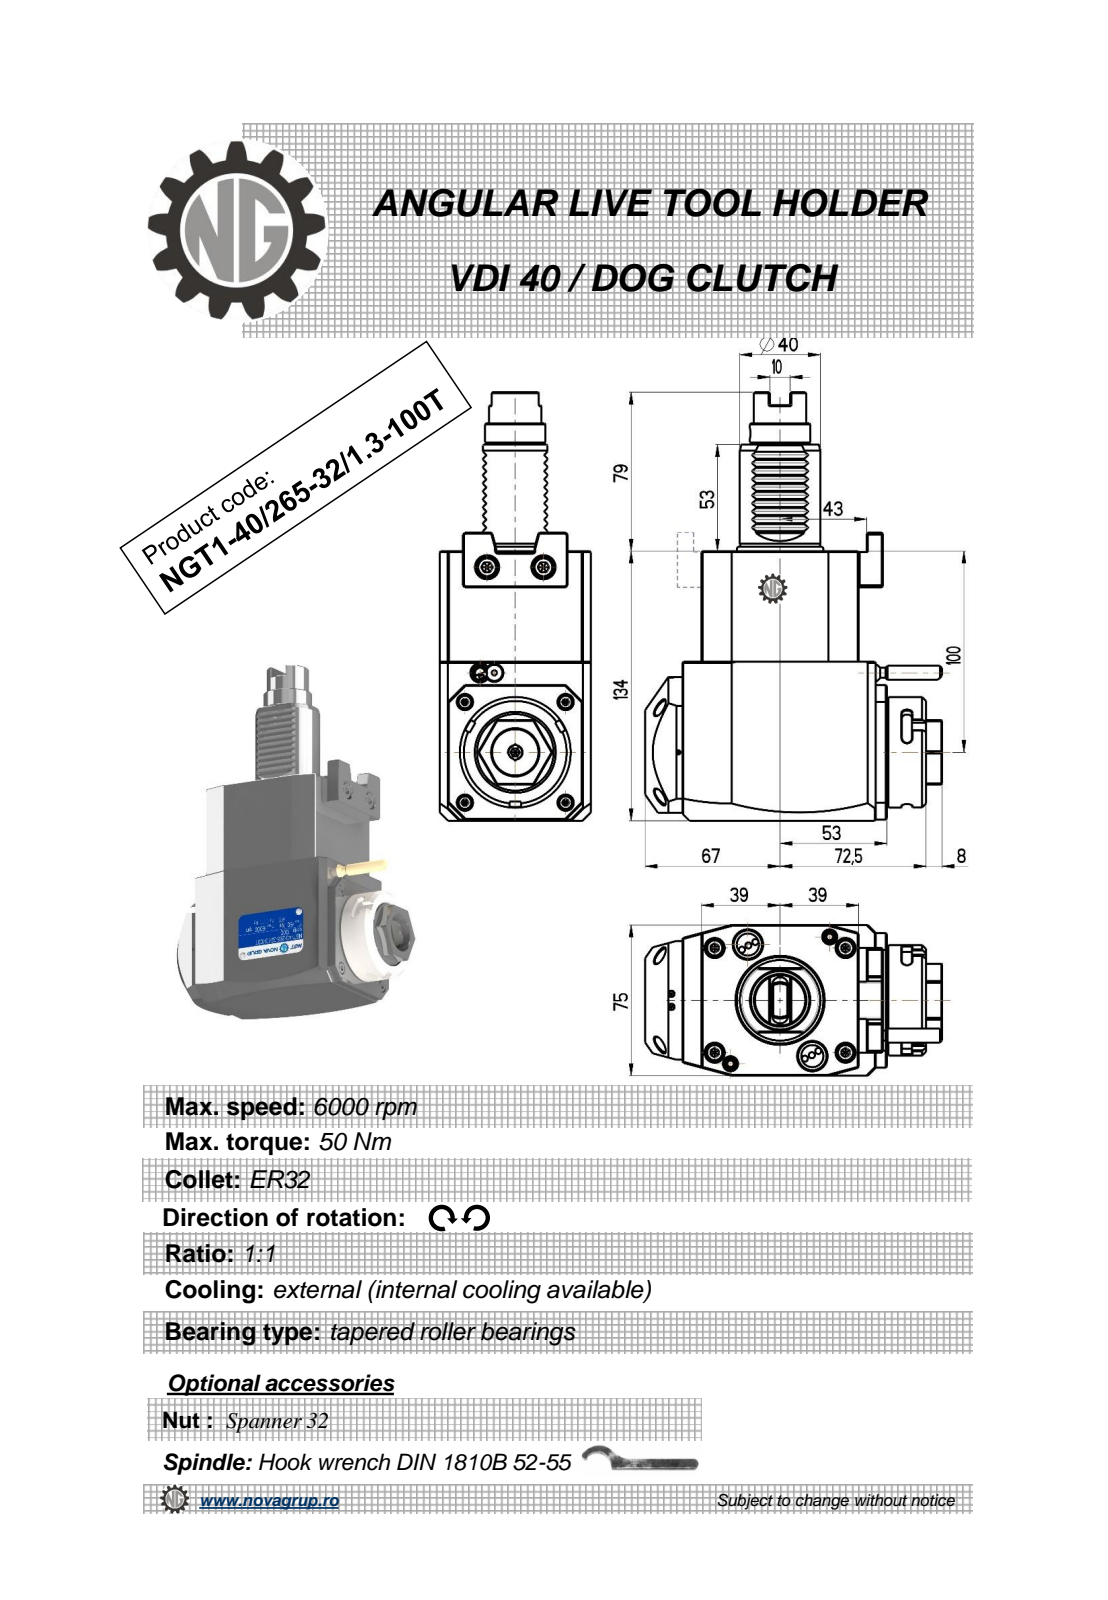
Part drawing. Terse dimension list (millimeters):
name: NGT1_40_265_32_1_3_100T
written by: PRO/ENGINEER BY PARAMETRIC TECHNOLOGY CORPORATION, 2010280 (CONFIG_CONTROL_DESIGN)
unit: mm
bodies: 1 solid, 383 faces (245 planar, 72 cylindrical, 66 other)
size: 213 × 147.5 × 75
volume: 1 079 000 mm³; area: 78 154 mm²
holes: 1× ⌀2.5, 1× ⌀3, 1× ⌀4.2, 1× ⌀23
bosses: 1× ⌀55, 1× ⌀48, 1× ⌀40, 1× ⌀30, 1× ⌀26, 1× ⌀8, 1× ⌀7, 1× ⌀5
rounds: 20× R0.3, 6× R0.26, 6× R2.5, 2× R0.5, 2× R1, 2× R180, 1× R12.5, 1× R24.5
face distances: 75, 134, 78, 14, 92, 19.5, 84.88, 21.5, 111.5, 33.5
hole spacings: 43.2, 120.28, 158.5
